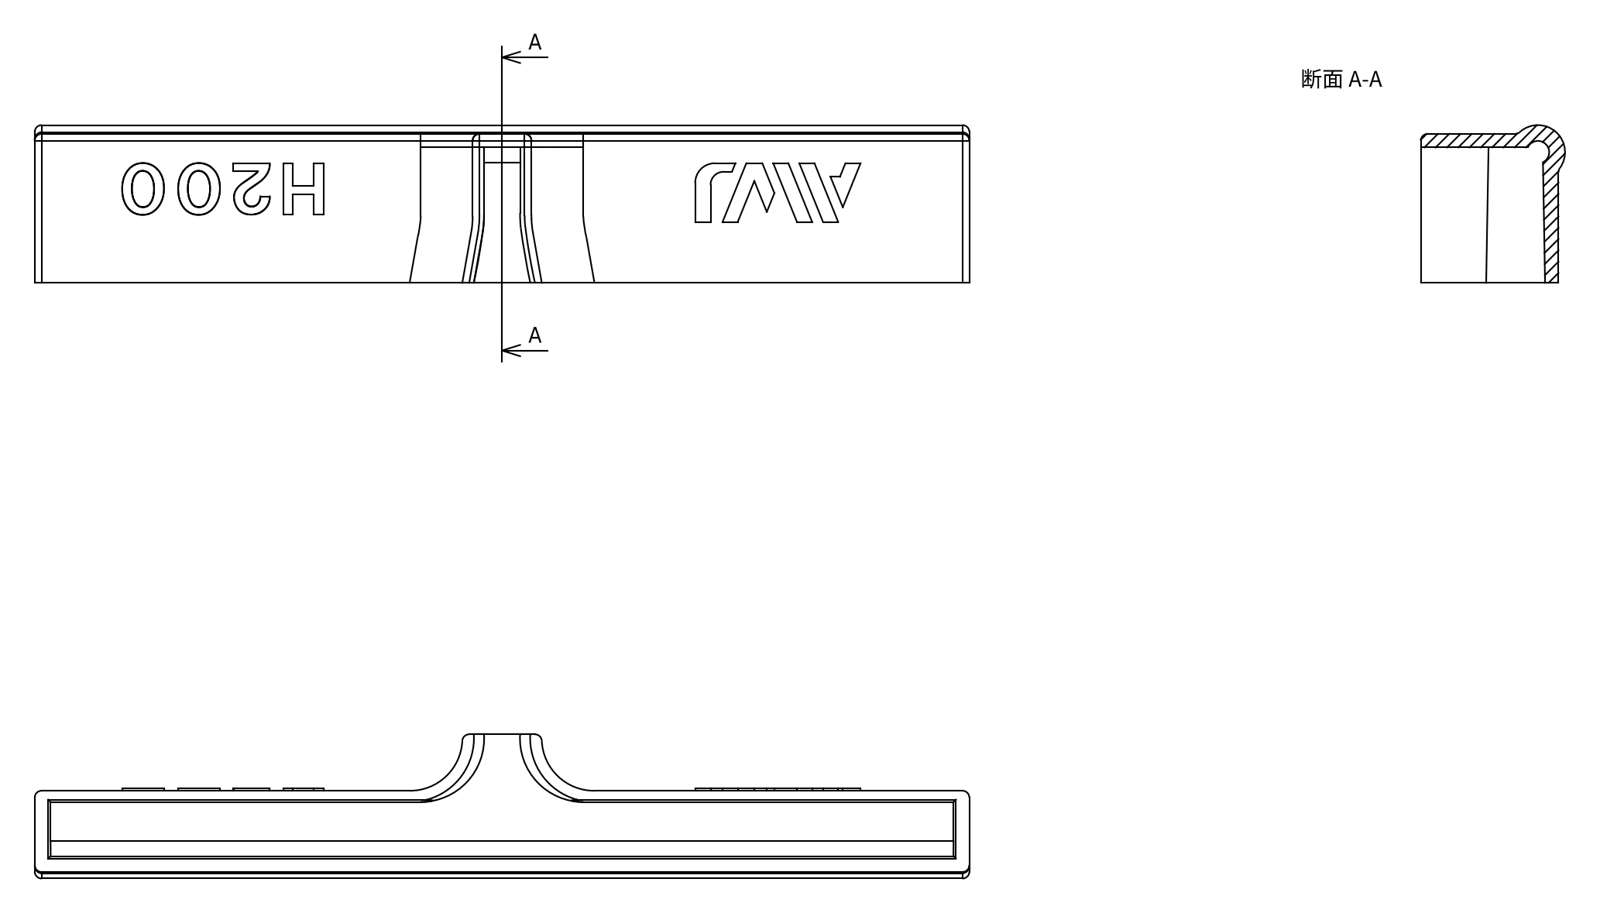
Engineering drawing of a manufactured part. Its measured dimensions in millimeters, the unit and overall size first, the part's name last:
Units: millimetres
Overall size (bounding box): 207 × 36.71 × 31.94
Partial cylindrical surfaces — rounded edges, fillets, slot ends (radius × count): R1.5 ×12, R2.5 ×1, R2.89 ×1, R4.33 ×1, R6 ×1
Main face-to-face distances: 18, 3, 30, 33, 207, 18.5, 0.5, 5.35, 3.12, 30.5
Volume: 51 349 mm³ · Surface area: 37 179 mm²
Bodies: 6 solids, 125 faces (72 planar, 19 cylindrical, 34 other)
STEP written by: Spatial InterOp 3D (CONFIG_CONTROL_DESIGN)
